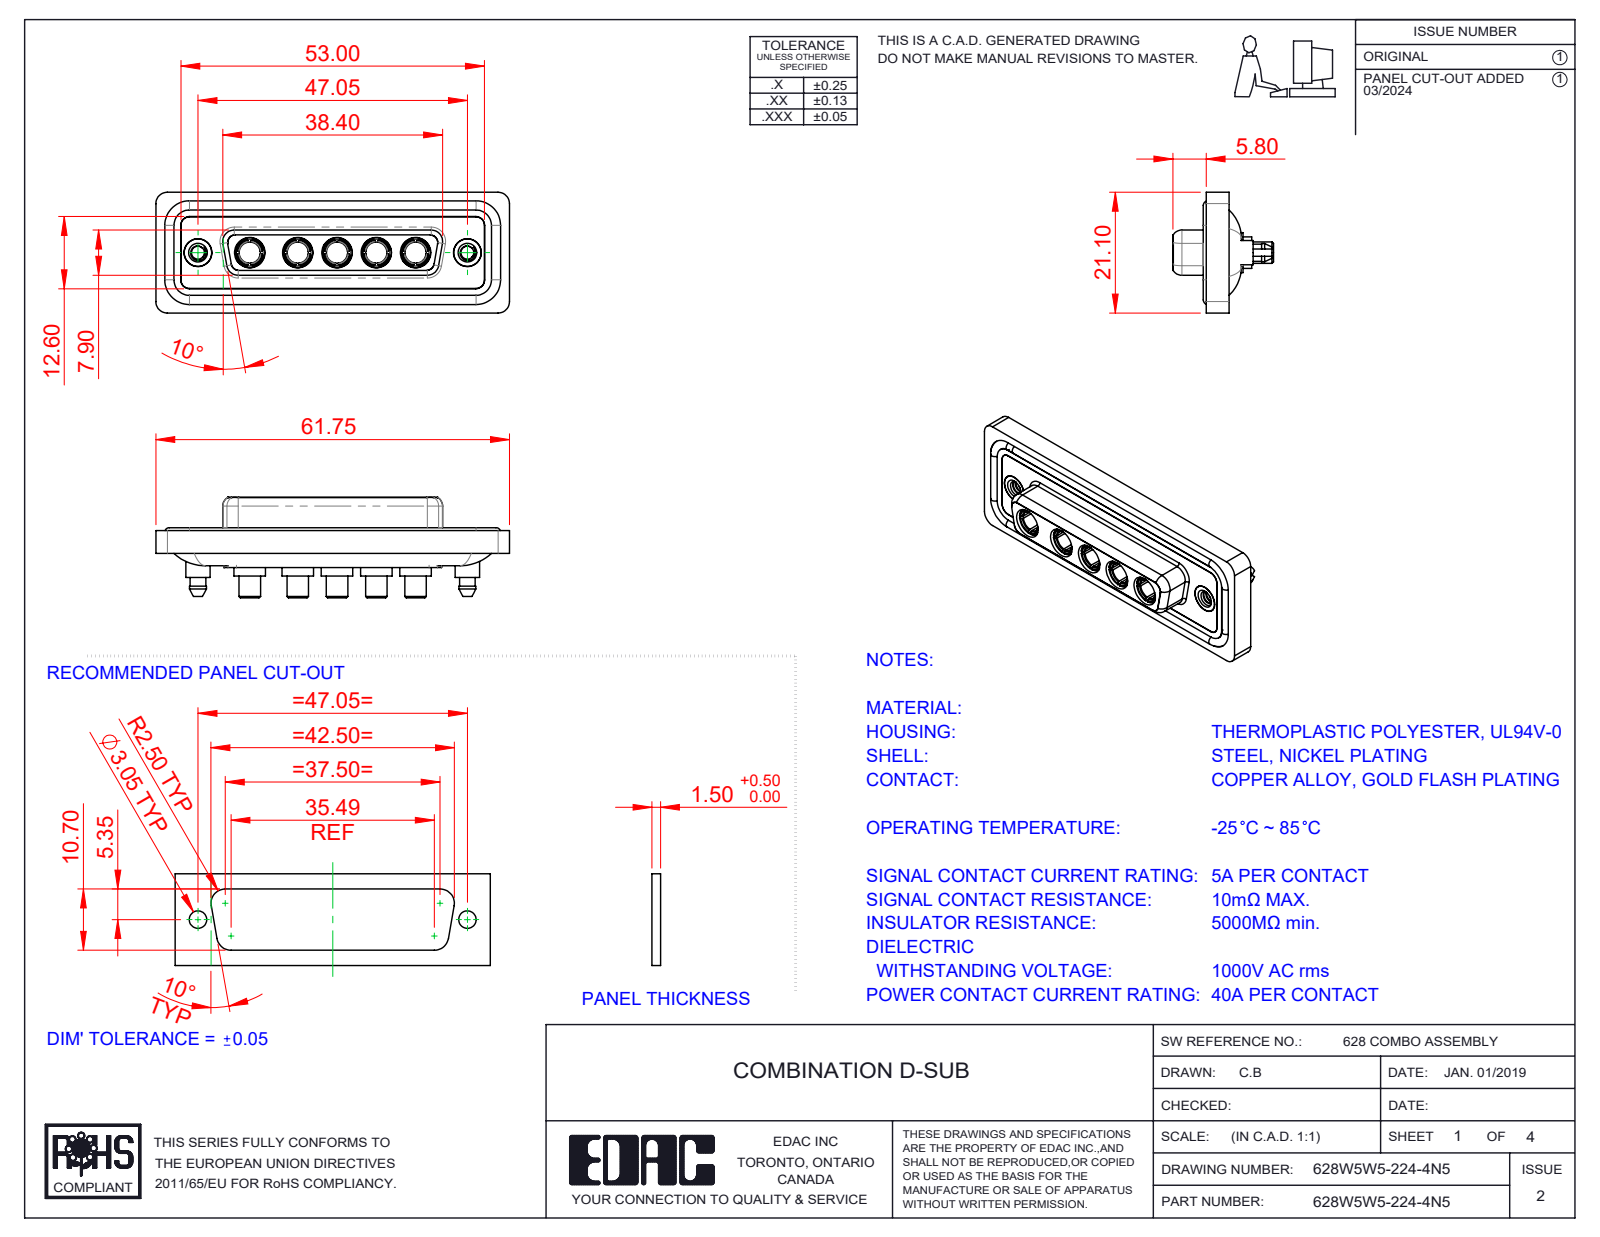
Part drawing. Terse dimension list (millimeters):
name: 628Combo Waterproof Housing_25 Contacts; 628W5W5-224-4N5; Power Socket_40A S; 628Combo Threaded Boardlock_5 (+3 more)
written by: SolidWorks 2023 (CONFIG_CONTROL_DESIGN)
unit: mm
bodies: 17 solids, 806 faces (266 planar, 335 cylindrical, 205 other)
size: 61.75 × 21.1 × 17.55
volume: 8 399 mm³; area: 13 803 mm²
holes: 7× ⌀4.85, 5× ⌀3.7, 5× ⌀5.3, 2× ⌀2.26, 2× ⌀4, 2× ⌀4.05, 2× ⌀5
bosses: 5× ⌀5.5, 5× ⌀5.2, 5× ⌀4.96, 5× ⌀4.75, 5× ⌀3.75, 4× ⌀1.6, 2× ⌀5.4, 2× ⌀4.95
rounds: 24× R1.5, 18× R2, 10× R1.6, 8× R1.35, 5× R2.1, 4× R0.25, 4× R0.5, 4× R0.6
face distances: 0.4, 1.8, 7.45, 5.65, 0.5, 7.05, 6.6, 1.6, 1.1, 2.9
hole spacings: 6.86, 9.04, 13.72, 38.01, 8.39, 15.25, 15.9, 17.43
